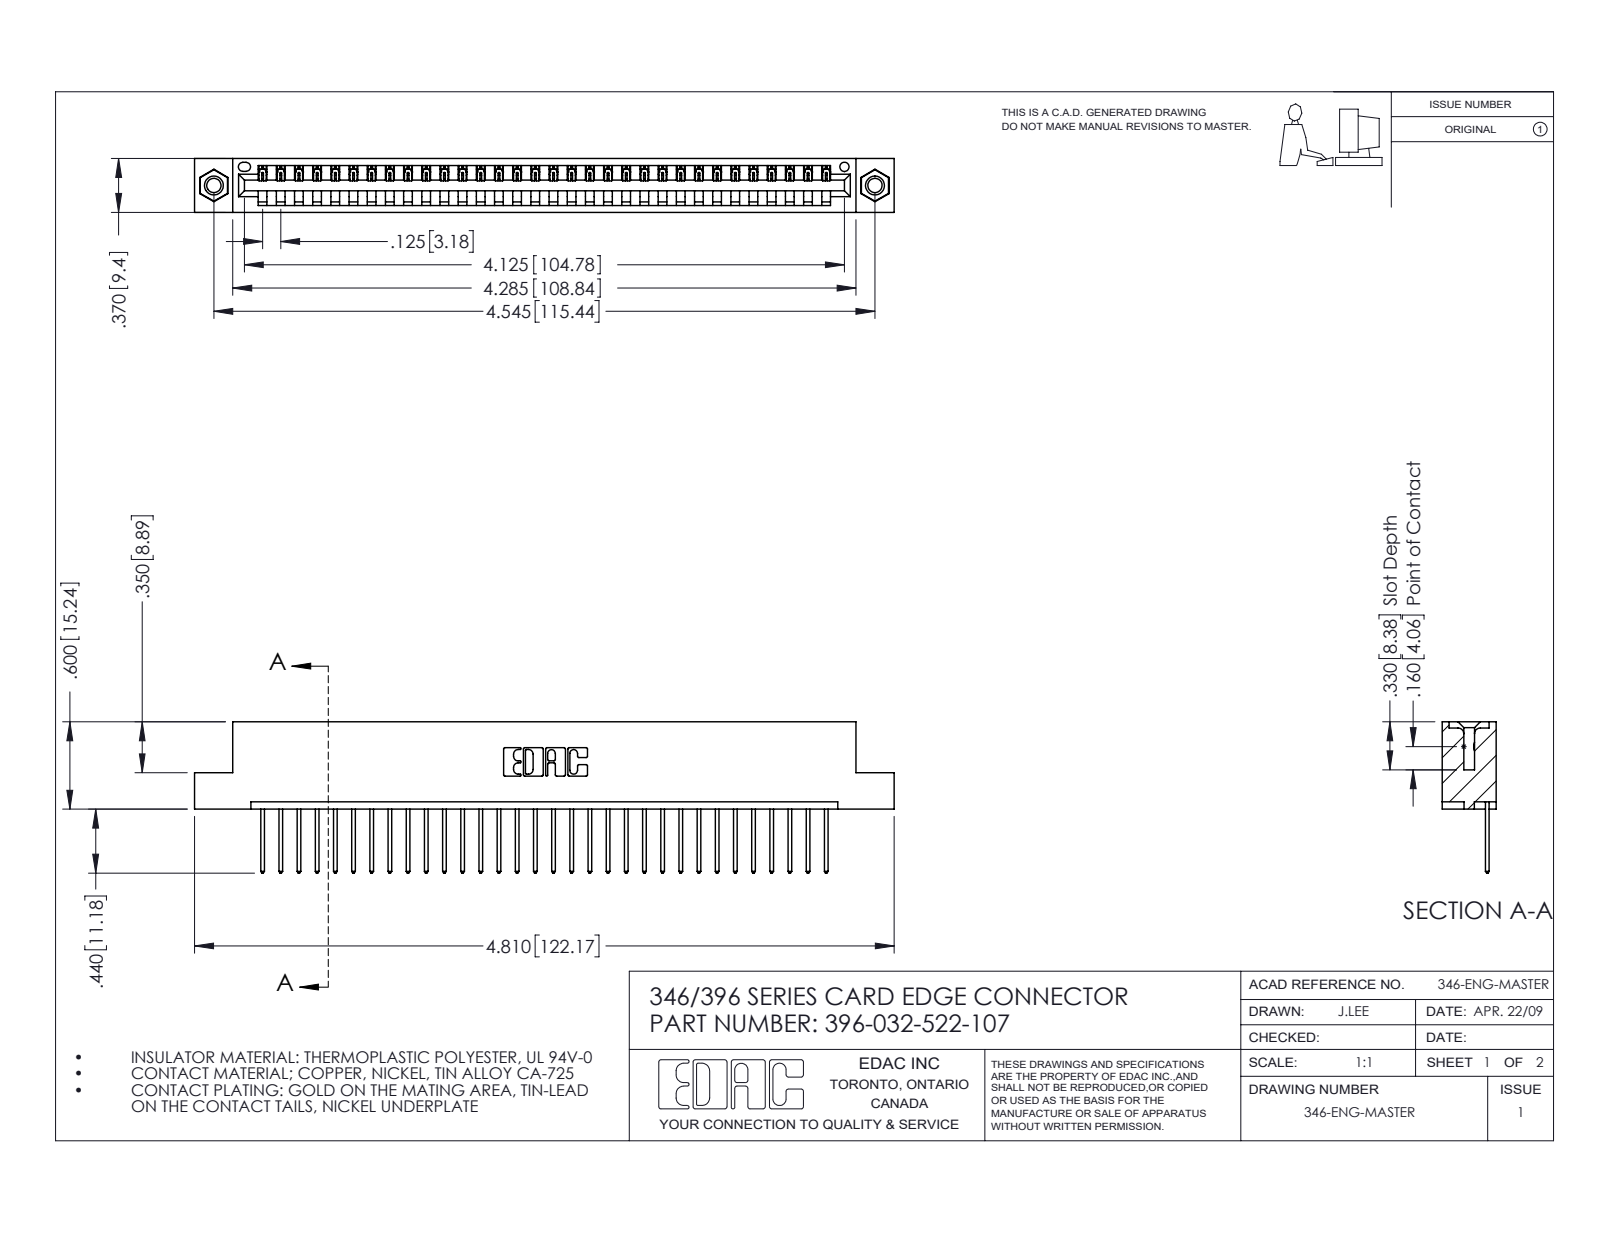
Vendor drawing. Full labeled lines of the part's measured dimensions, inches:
Part name (STEP PRODUCT): 346 Part_Flush Mounting Lugs - 0.156 Dia-TI; 345-292-001_345-293-122; 345-250-001_345-250-005-103; 396-032-522-107
STEP written by: SolidWorks 2016 (CONFIG_CONTROL_DESIGN)
Units: inches
Bodies: 35 solids, 2038 faces (1388 planar, 634 cylindrical, 16 other)
Overall size (bounding box): 4.81 × 1.04 × 0.37
Volume: 0.709 in³ · Surface area: 22.57 in²
Round holes (diameter × count): ⌀0.098 ×2, ⌀0.125 ×2, ⌀0.156 ×2, ⌀0.064 ×1
Round bosses / shafts (diameter × count): ⌀0.155 ×2
Partial cylindrical surfaces — rounded edges, fillets, slot ends (radius × count): R0.006 ×64, R0.01 ×64, R0.01 ×22, R0.007 ×6, R0.031 ×6, R0.026 ×3, R0.031 ×2, R0.04 ×2
Main face-to-face distances: 0.048, 0.322, 0.37, 0.25, 0.072, 0.298, 0.025, 0.148, 0.222, 0.1
Hole centre spacings: 0.246, 4.337, 4.545
